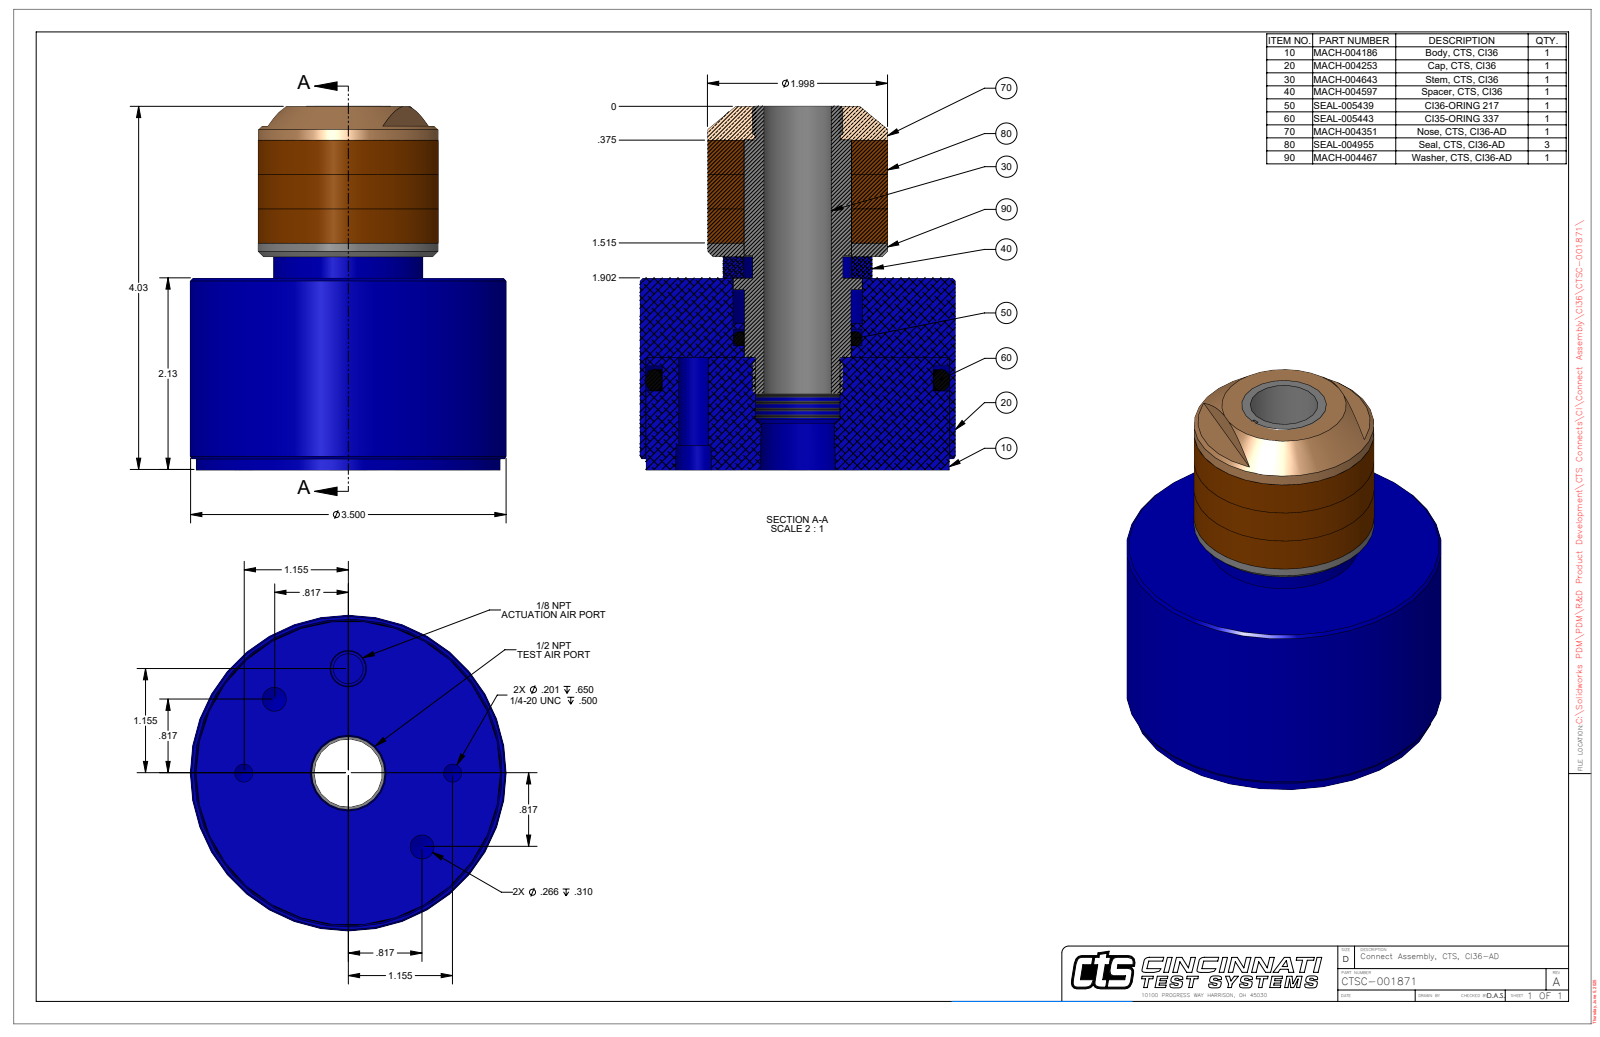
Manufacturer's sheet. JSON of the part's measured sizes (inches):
{"part_name": "CTSC-001871", "step_written_by": "SolidWorks 2023 (AUTOMOTIVE_DESIGN)", "units": "inches", "bodies": {"solids": 1, "faces": 75, "planar": 20, "cylindrical": 29, "other": 26}, "overall_size": [4.032, 3.5, 3.5], "volume_in3": 23.7, "surface_area_in2": 81.59, "round_holes": [[0.201, 2], [0.266, 2], [0.332, 1], [0.75, 1], [0.937, 1], [1.438, 1], [3.373, 1]], "round_bosses_or_shafts": [[3.5, 1], [3.365, 1], [1.998, 1], [1.656, 1], [1.427, 1]], "partial_cylinders_radius": [[0.461, 1]], "face_to_face_distances": [2.125, 4.027, 1.902, 2.362, 0.237, 1.665, 3.808, 1.683, 1.446, 0.219], "hole_center_spacings": [0.884, 1.155, 2.134, 1.155, 1.633, 2.309, 2.31]}
